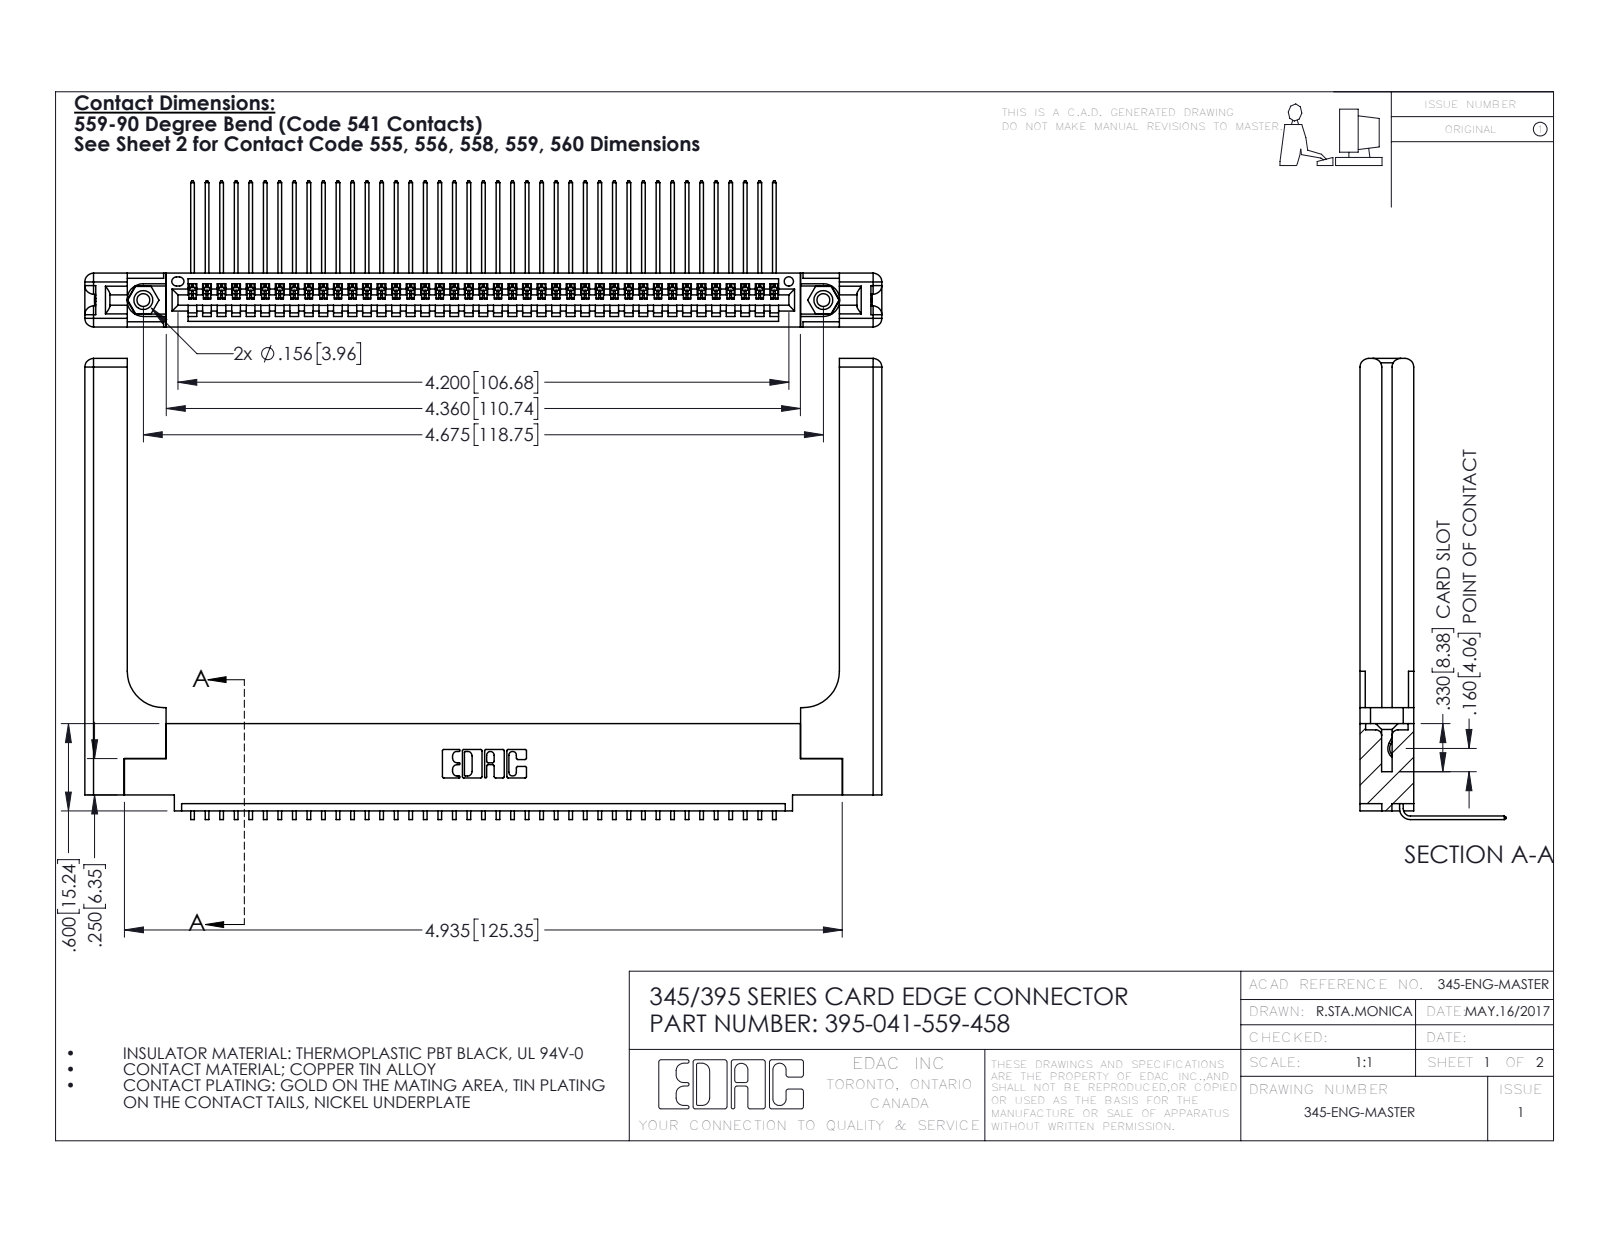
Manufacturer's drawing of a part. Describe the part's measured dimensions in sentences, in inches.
The part is named "345-220-058_345-220-058; 345-292-001_558 559 Tail - 1; 345 Part_0.110 Offset - 0.156 Dia-TH; 345-250-001_345-250-001-102 (+1 more)". Its 3-D file was written by "SolidWorks 2016 (CONFIG_CONTROL_DESIGN)". It is 46 solids with 2846 faces: 1954 planar, 832 cylindrical and 60 other. Overall it measures 5.479 by 3.169 by 1.005 inches. Its volume is 1.329 cubic inches and its surface area 36.91 square inches. Round holes: 2 of diameter 0.089, 2 of diameter 0.125, 2 of diameter 0.156, 1 of diameter 0.064. Round bosses or shafts: 2 of diameter 0.155. Partial cylindrical surfaces (rounded edges, fillets, slot ends): 82 of radius 0.006, 22 of radius 0.01, 16 of radius 0.06, 6 of radius 0.007, 6 of radius 0.031, 3 of radius 0.026, 2 of radius 0.03, 2 of radius 0.031. The main face-to-face distances are 0.37, 0.072, 0.298, 0.2, 0.098, 0.272, 0.025, 0.148, 0.15, 0.225. The hole center spacings are 0.27, 4.439, 4.675.
